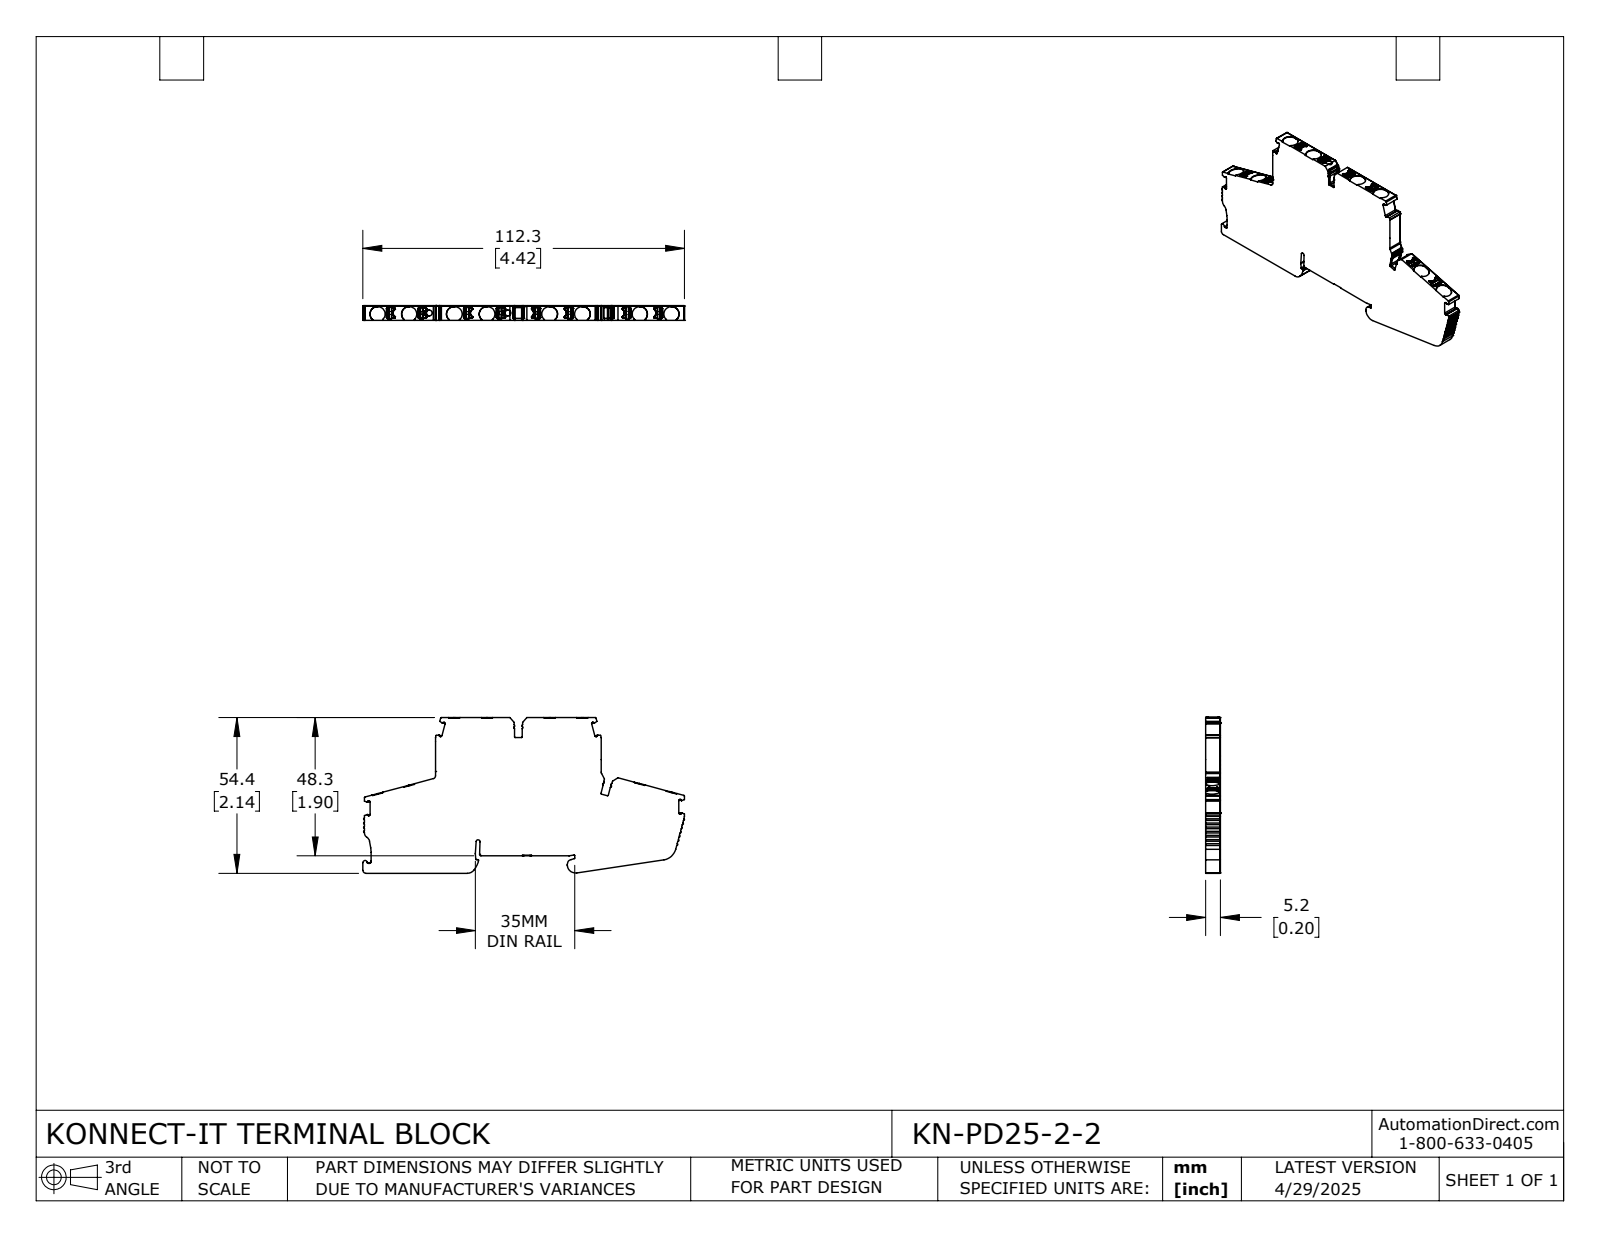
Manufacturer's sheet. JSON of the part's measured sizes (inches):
{"part_name": "KN-PD25-2-2", "step_written_by": "SolidWorks 2024 (CONFIG_CONTROL_DESIGN)", "units": "inches", "bodies": {"solids": 1, "faces": 1052, "planar": 494, "cylindrical": 422, "other": 136}, "overall_size": [4.422, 2.141, 0.203], "volume_in3": 1.357, "surface_area_in2": 16.61, "round_holes": [[0.083, 2]], "partial_cylinders_radius": [[0.008, 98], [0.012, 40], [0.004, 37], [0.006, 32], [0.02, 17], [0.1, 16], [0.016, 10], [0.006, 8]], "face_to_face_distances": [0.203, 0.24, 2.141, 1.9, 1.893, 2.133, 2.279, 0.079, 0.197, 4.322]}
